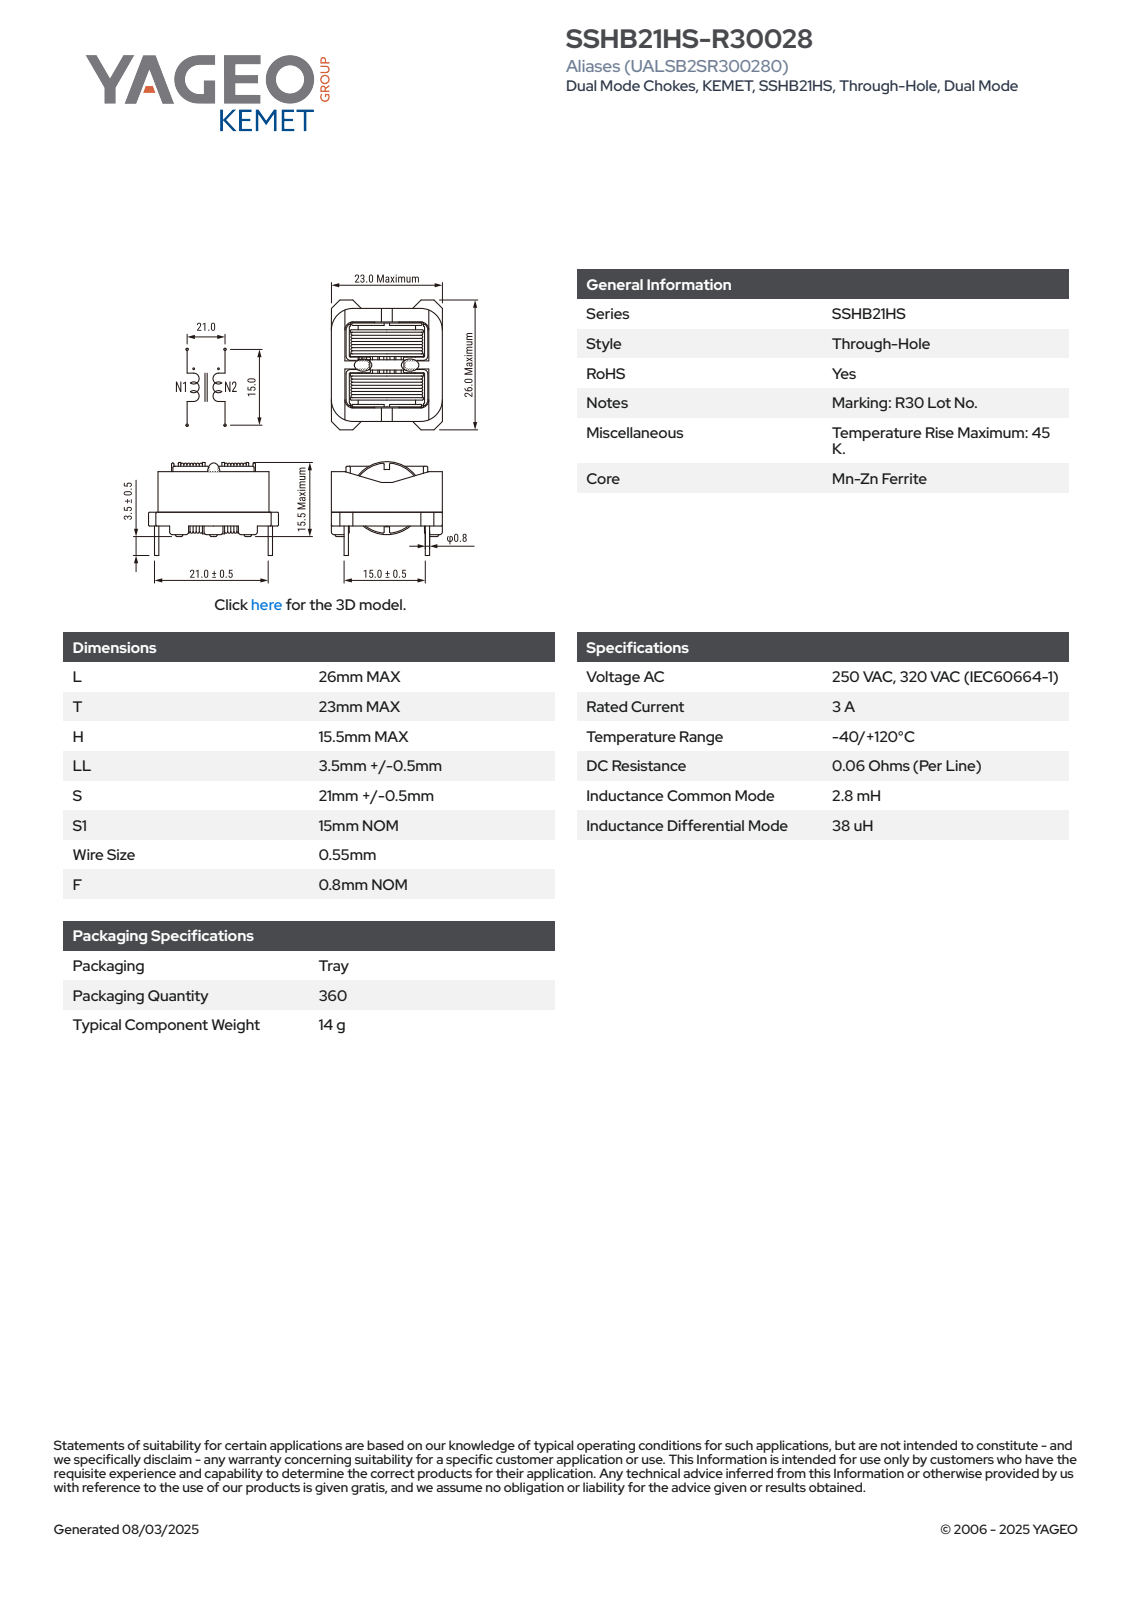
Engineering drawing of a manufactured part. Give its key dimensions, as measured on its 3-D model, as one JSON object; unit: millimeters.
{"part_name": "SSHB21HS(MAX-LOGO)", "step_written_by": "SolidWorks 2018 (AUTOMOTIVE_DESIGN)", "units": "millimeters", "bodies": {"solids": 1, "faces": 534, "planar": 364, "cylindrical": 120, "other": 50}, "overall_size": [26, 23, 19], "volume_mm3": 4547, "surface_area_mm2": 5006, "round_holes": [[5.4, 1]], "round_bosses_or_shafts": [[0.8, 4], [13.5, 1], [13, 1], [10.6, 1], [6.3, 1]], "partial_cylinders_radius": [[0.2, 22], [0.5, 10], [0.8, 8], [0.3, 4], [1.3, 4], [1.5, 4], [4, 4], [2.6, 1]], "face_to_face_distances": [0.6, 3.95, 2.7, 0.65, 4.55, 18.45, 8.9, 10.05, 18.2, 0.8]}
